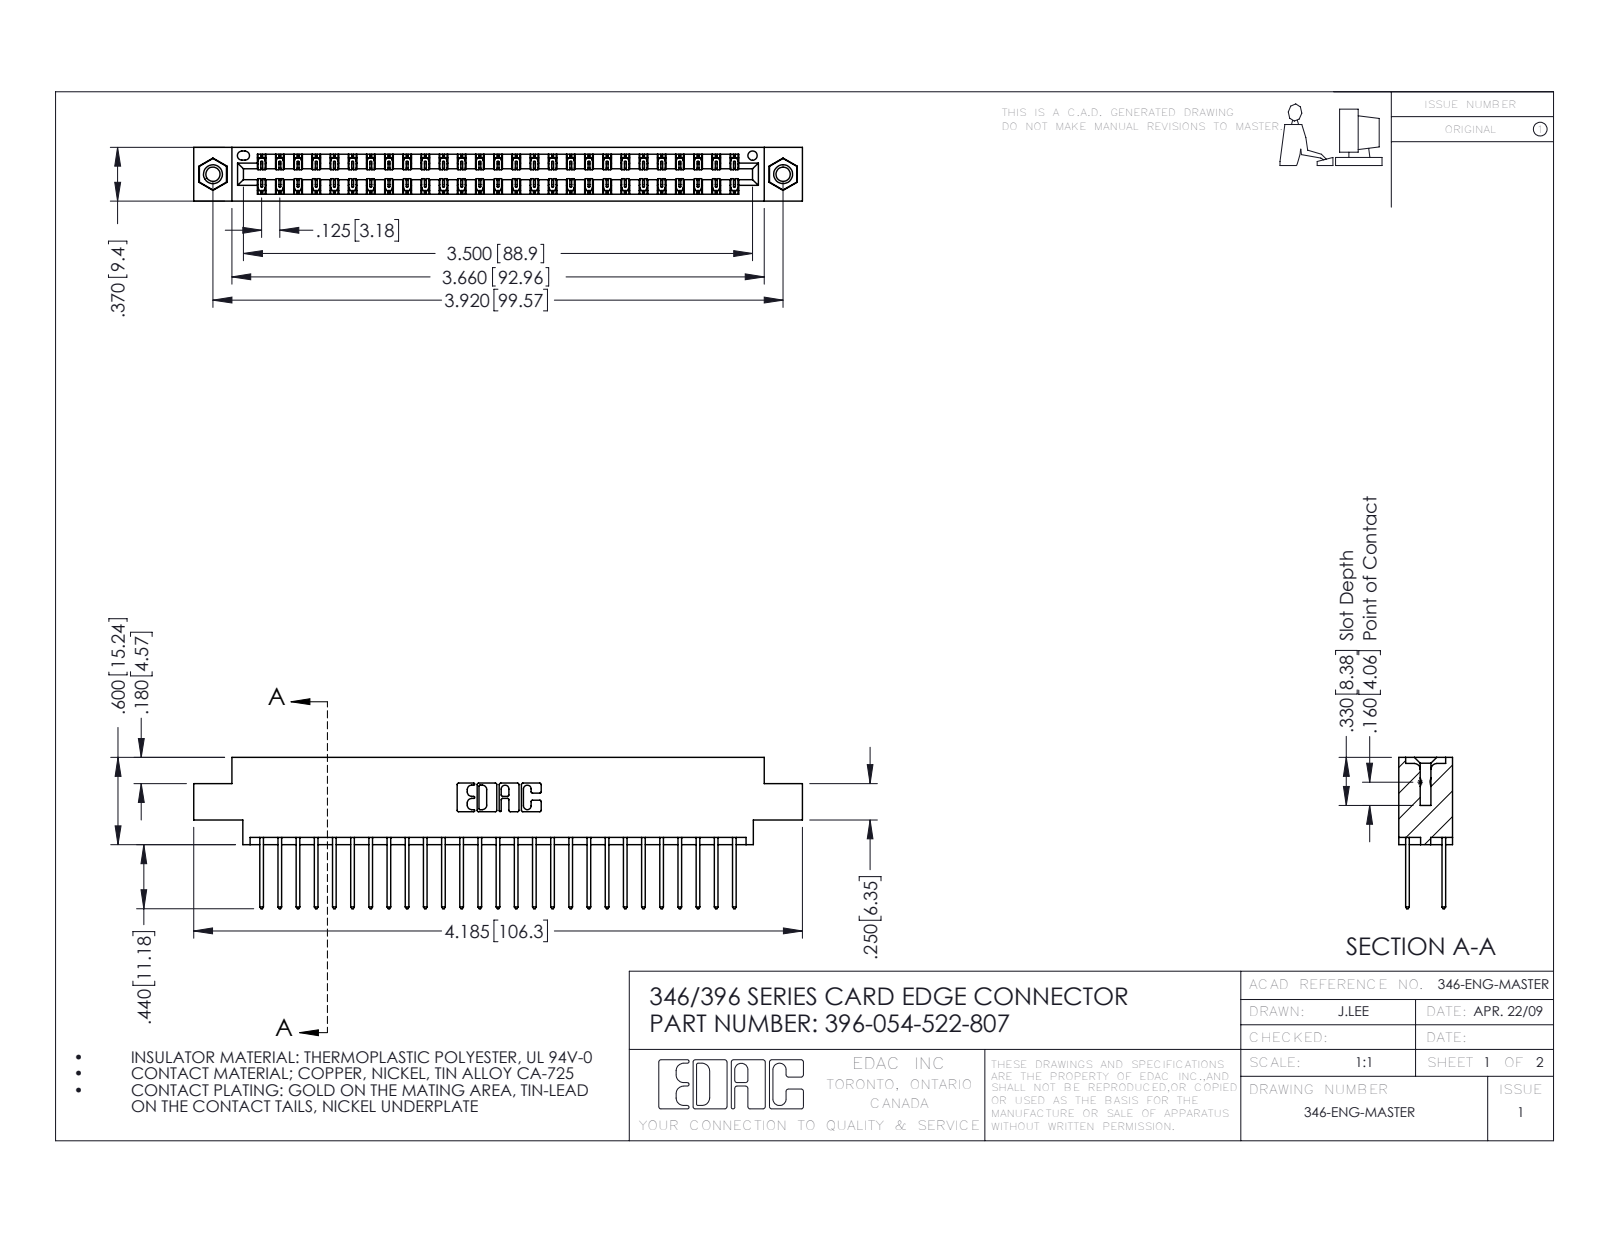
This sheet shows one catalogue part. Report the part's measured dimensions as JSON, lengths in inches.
{"part_name": "345-250-001_345-250-005-103; 396-054-522-807; 345-292-001_345-293-122; 346 Part_0.170 Offset - 0.156 Dia-TI", "step_written_by": "SolidWorks 2016 (CONFIG_CONTROL_DESIGN)", "units": "inches", "bodies": {"solids": 57, "faces": 2994, "planar": 2002, "cylindrical": 976, "other": 16}, "overall_size": [4.185, 1.04, 0.37], "volume_in3": 0.624, "surface_area_in2": 22.73, "round_holes": [[0.098, 2], [0.125, 2], [0.156, 2], [0.064, 1]], "round_bosses_or_shafts": [[0.155, 2]], "partial_cylinders_radius": [[0.006, 81], [0.01, 54], [0.01, 22], [0.007, 6], [0.031, 6], [0.026, 3], [0.014, 2], [0.022, 2]], "face_to_face_distances": [0.048, 0.322, 0.25, 0.37, 0.072, 0.298, 0.025, 0.275, 0.222, 0.148], "hole_center_spacings": [0.246, 3.712, 3.92]}
